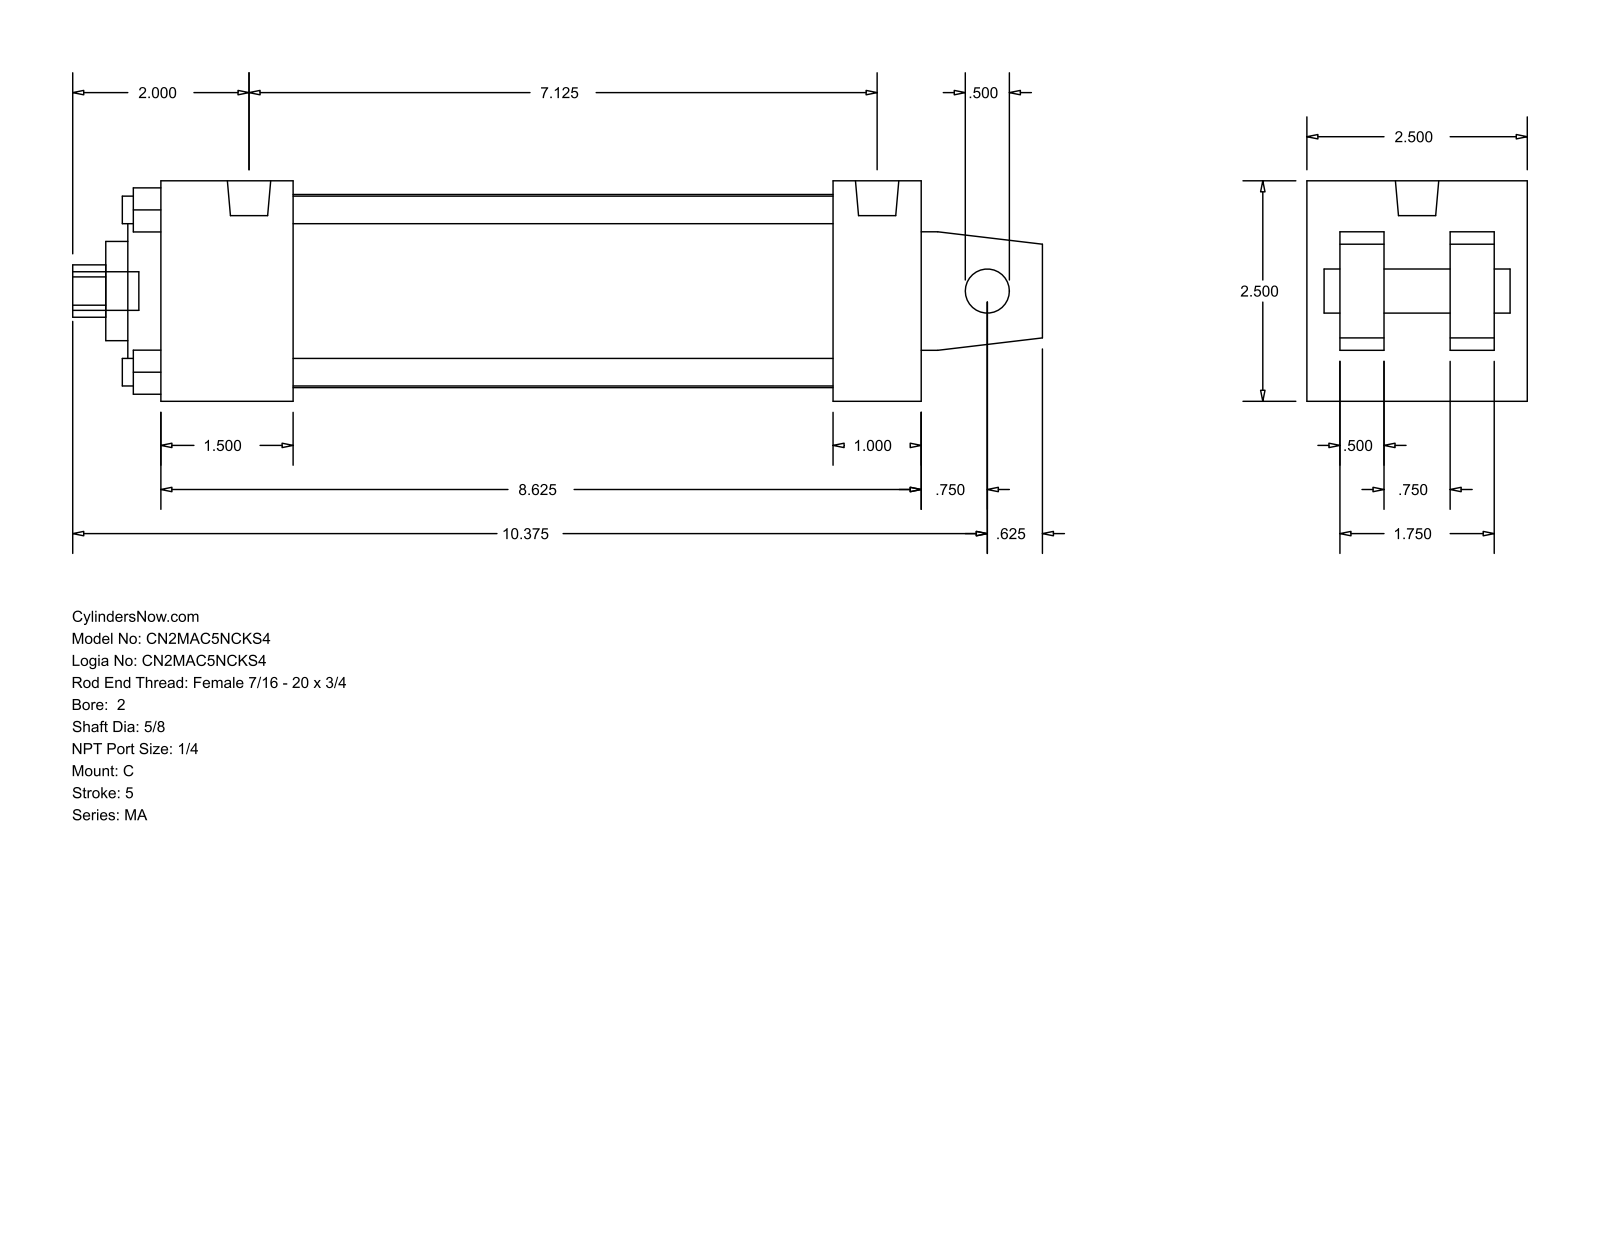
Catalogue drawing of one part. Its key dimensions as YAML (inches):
part_name: "MA_C__0200_0.625"
step_written_by: "GSSL Pune (CONFIG_CONTROL_DESIGN)"
units: inches
bodies: {solids: 0, faces: 105, planar: 77, cylindrical: 28, other: 0}
overall_size: [11, 2.5, 2.5]
round_holes:
  - {diameter: 0.313, count: 4}
  - {diameter: 0.5, count: 1}
  - {diameter: 0.625, count: 1}
  - {diameter: 1.125, count: 1}
  - {diameter: 2, count: 1}
  - {diameter: 2.19, count: 1}
round_bosses_or_shafts:
  - {diameter: 0.313, count: 4}
  - {diameter: 0.492, count: 2}
  - {diameter: 0.437, count: 1}
partial_cylinders:
  - {radius: 0.297, count: 1}
face_to_face_distances: [2.5, 0.375, 0.5, 0.875, 1.625, 2.125, 1.25, 1, 1.5, 8.625]
hole_center_spacings: [1.301, 1.84, 2.602]
